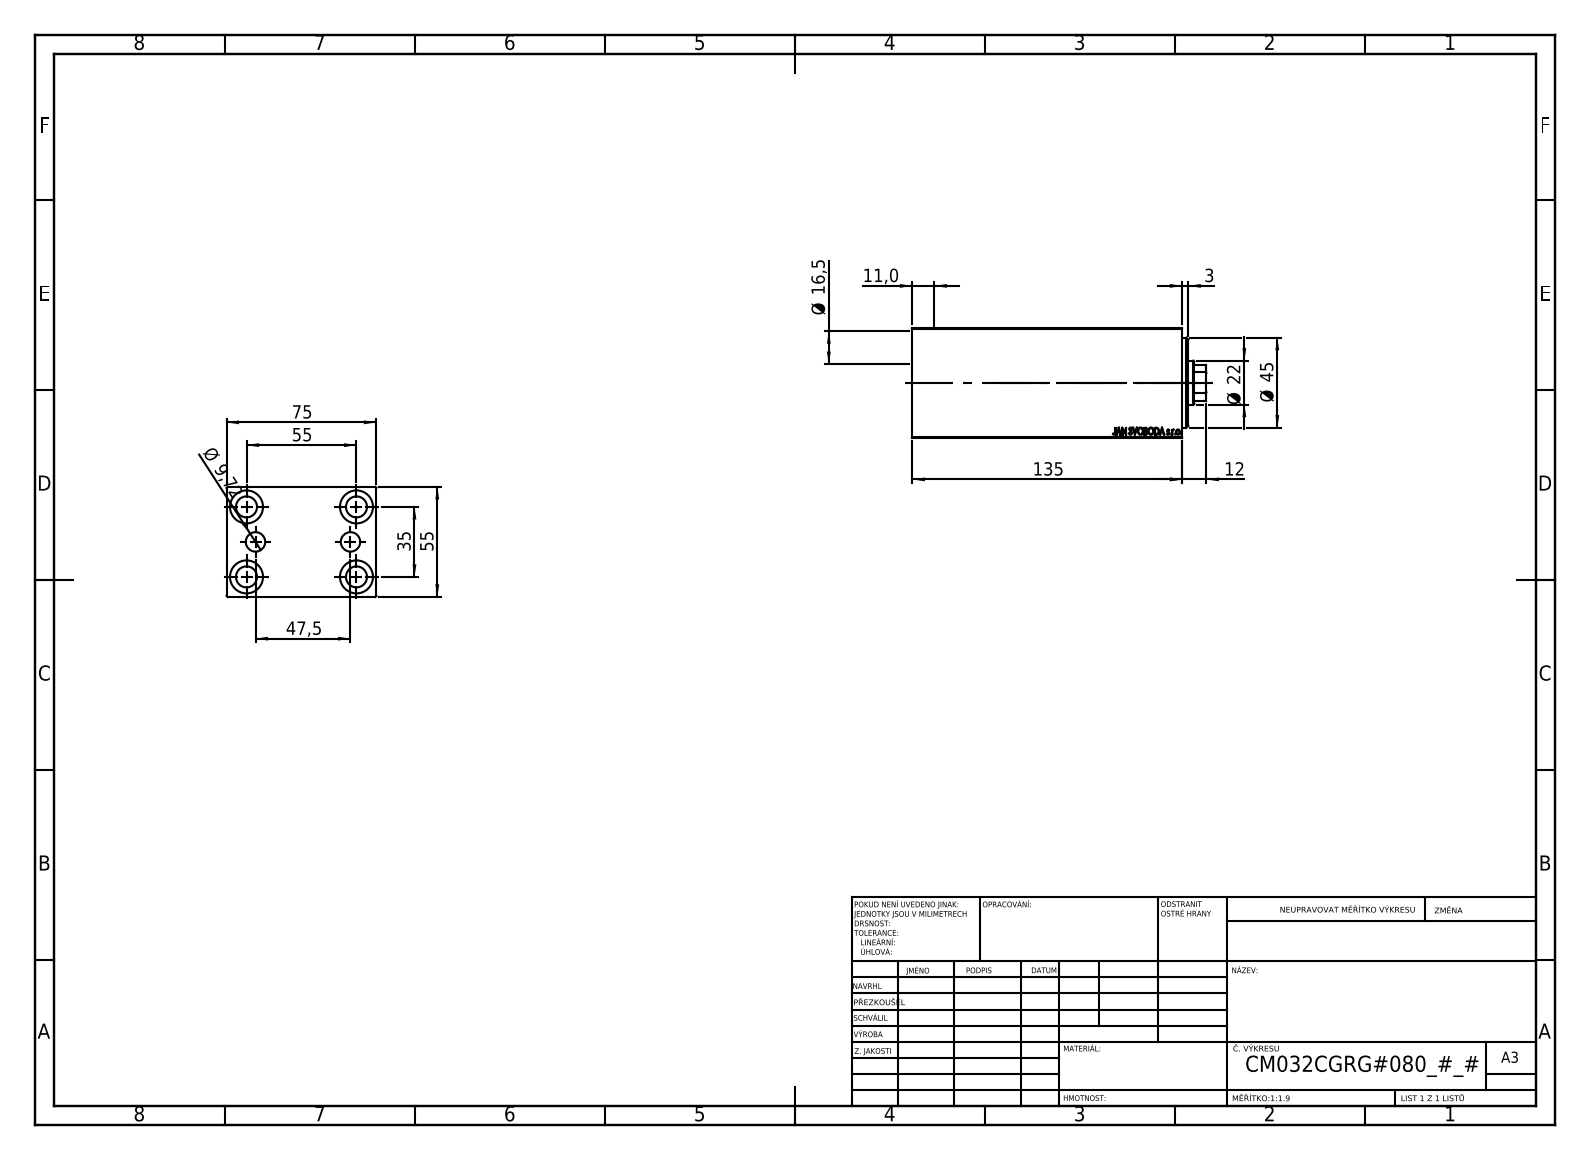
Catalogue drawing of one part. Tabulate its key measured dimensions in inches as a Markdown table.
| quantity | value |
| --- | --- |
| part name | V450CM_C_Body; V450CM_C_VCP; V450CM_VC_B |
| STEP written by | SolidWorks 2019 (CONFIG_CONTROL_DESIGN) |
| units | inches |
| bodies | 3 solids, 852 faces (406 planar, 52 cylindrical, 394 other) |
| overall size | 5.787 × 2.953 × 2.165 |
| volume | 28.63 in³ |
| surface area | 144.7 in² |
| round holes (diameter × count) | 0.413 × 5, 0.65 × 4, 0.383 × 2, 0.866 × 1, 1.004 × 1, 1.26 × 1, 1.339 × 1, 1.772 × 1 |
| partial cylindrical surfaces (radius × count) | 0.413 × 1 |
| main face-to-face distances | 2.165, 2.953, 0.394, 4.921, 5.315, 5.118, 0.197, 4.724, 4.449, 0.433 |
| hole center spacings | 1.283, 0.699, 0.711, 1.378, 2.104, 2.16, 2.165, 2.567 |
